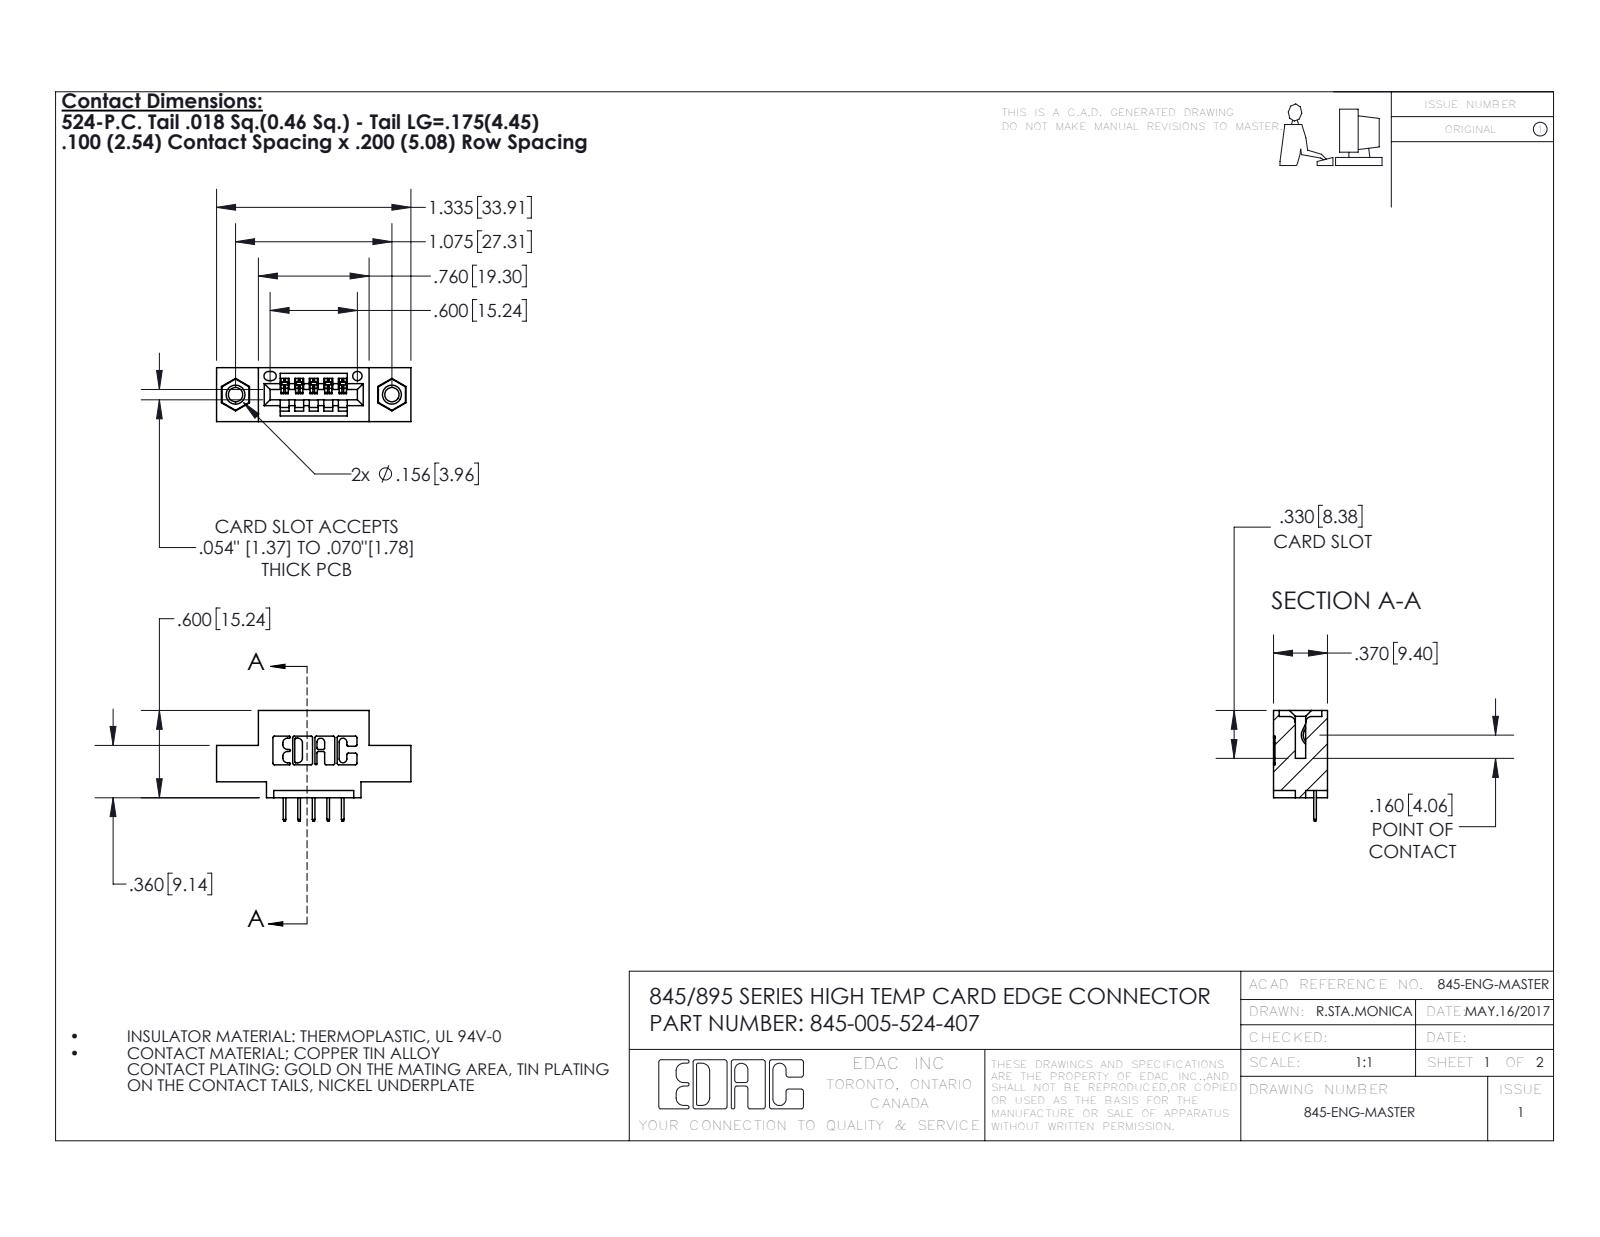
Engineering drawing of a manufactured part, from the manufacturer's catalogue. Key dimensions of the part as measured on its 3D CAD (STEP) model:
Part name (STEP PRODUCT): 345 Part_0.110 Offset - 0.156 Dia-TI; 345-005-524-407; 345-292-001_345-293-124; 345-250-001_345-250-005-103
STEP written by: SolidWorks 2016 (CONFIG_CONTROL_DESIGN)
Units: inches
Bodies: 8 solids, 500 faces (346 planar, 138 cylindrical, 16 other)
Overall size (bounding box): 1.335 × 0.762 × 0.37
Volume: 0.172 in³ · Surface area: 5.09 in²
Round holes (diameter × count): ⌀0.098 ×2, ⌀0.125 ×2, ⌀0.156 ×2, ⌀0.064 ×1
Round bosses / shafts (diameter × count): ⌀0.155 ×2
Partial cylindrical surfaces — rounded edges, fillets, slot ends (radius × count): R0.01 ×22, R0.006 ×10, R0.007 ×6, R0.031 ×6, R0.026 ×3, R0.031 ×2, R0.04 ×2, R0.014 ×1
Main face-to-face distances: 0.2, 0.37, 0.1, 0.072, 0.298, 0.025, 0.25, 0.06, 0.16, 0.04
Hole centre spacings: 0.27, 0.847, 1.075
